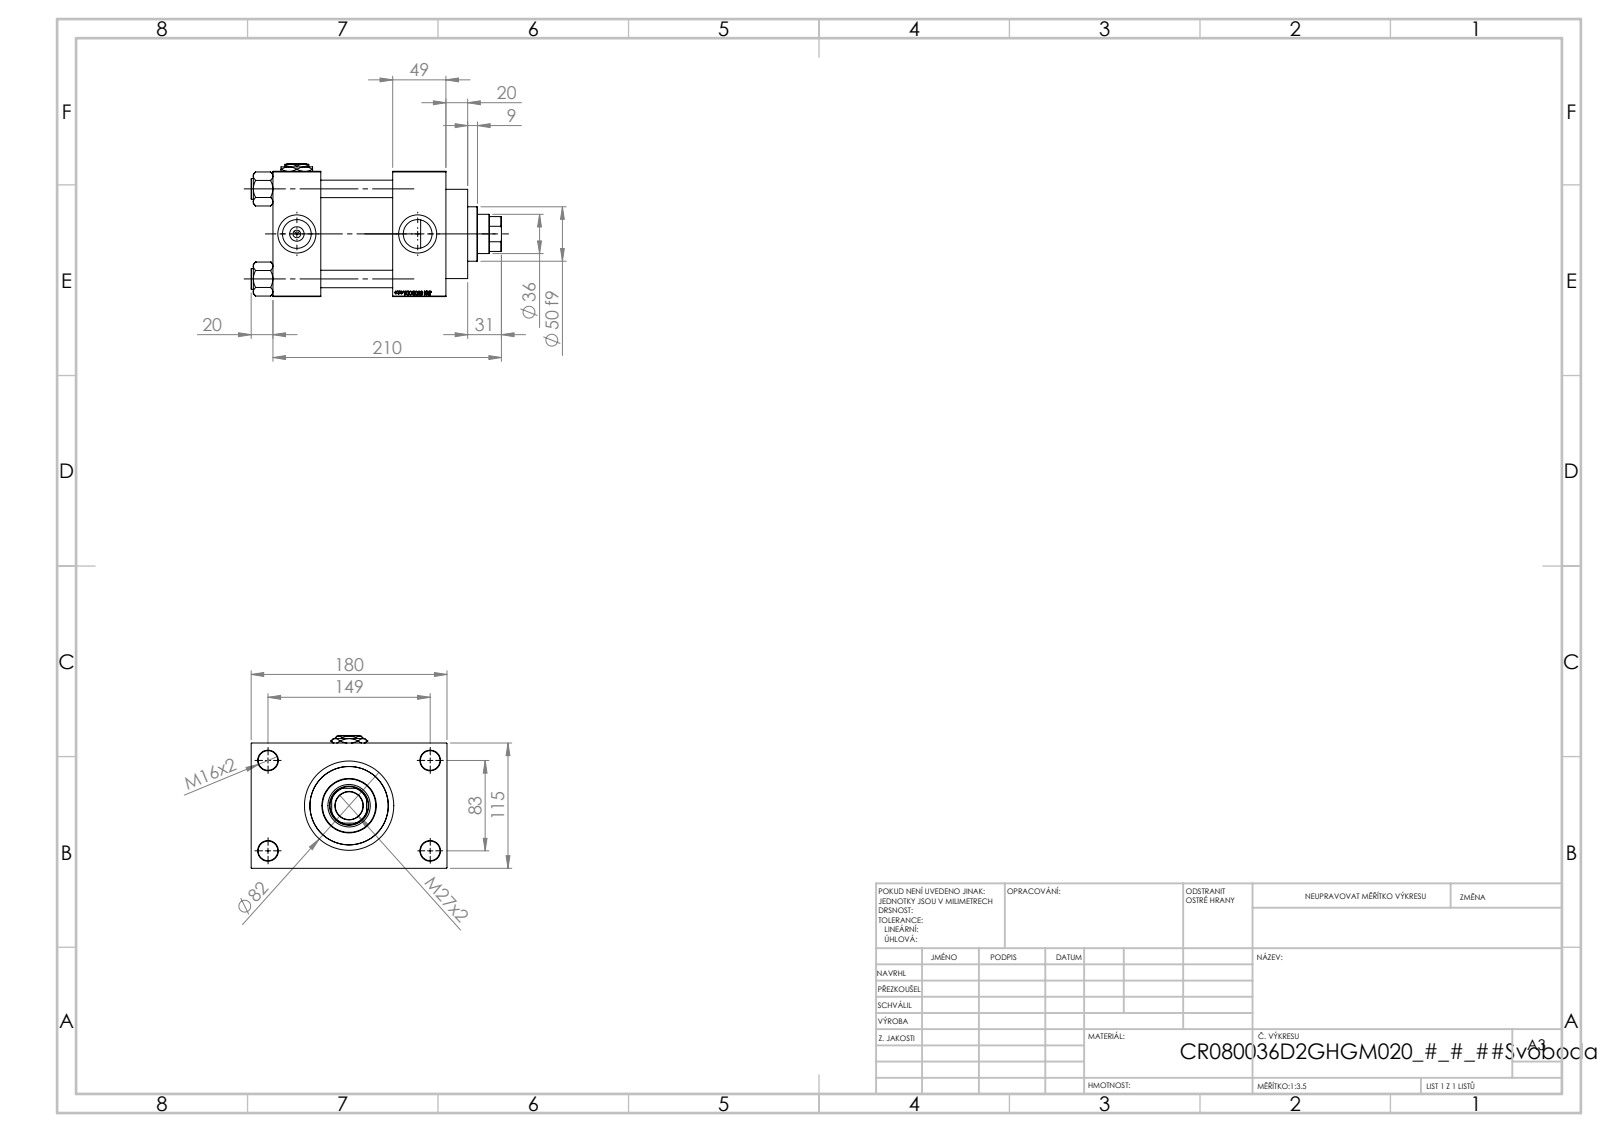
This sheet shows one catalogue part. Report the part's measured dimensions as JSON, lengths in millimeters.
{"part_name": "V215CR_VCP_D; Zatka_pro_OIL_PORT; NUT_M5_D; V215CR_D_TYCINKA (+2 more)", "step_written_by": "SolidWorks 2019 (CONFIG_CONTROL_DESIGN)", "units": "millimeters", "bodies": {"solids": 12, "faces": 1204, "planar": 569, "cylindrical": 95, "other": 540}, "overall_size": [230, 180, 122], "volume_mm3": 1976000, "surface_area_mm2": 300381, "round_holes": [[16, 4], [18, 4], [7, 3], [26.44, 3], [35, 3], [25.5, 1], [36, 1], [39, 1], [61, 1], [72, 1], [80, 1]], "round_bosses_or_shafts": [[19, 4], [86, 1], [82, 1], [50, 1]], "partial_cylinders_radius": [[17.5, 1]], "face_to_face_distances": [115, 66, 110, 49, 44, 159, 32.5, 147.5, 20, 69], "hole_center_spacings": [33.15, 58.48, 82.7, 85.28, 89.24, 115.85, 142.43, 83]}
